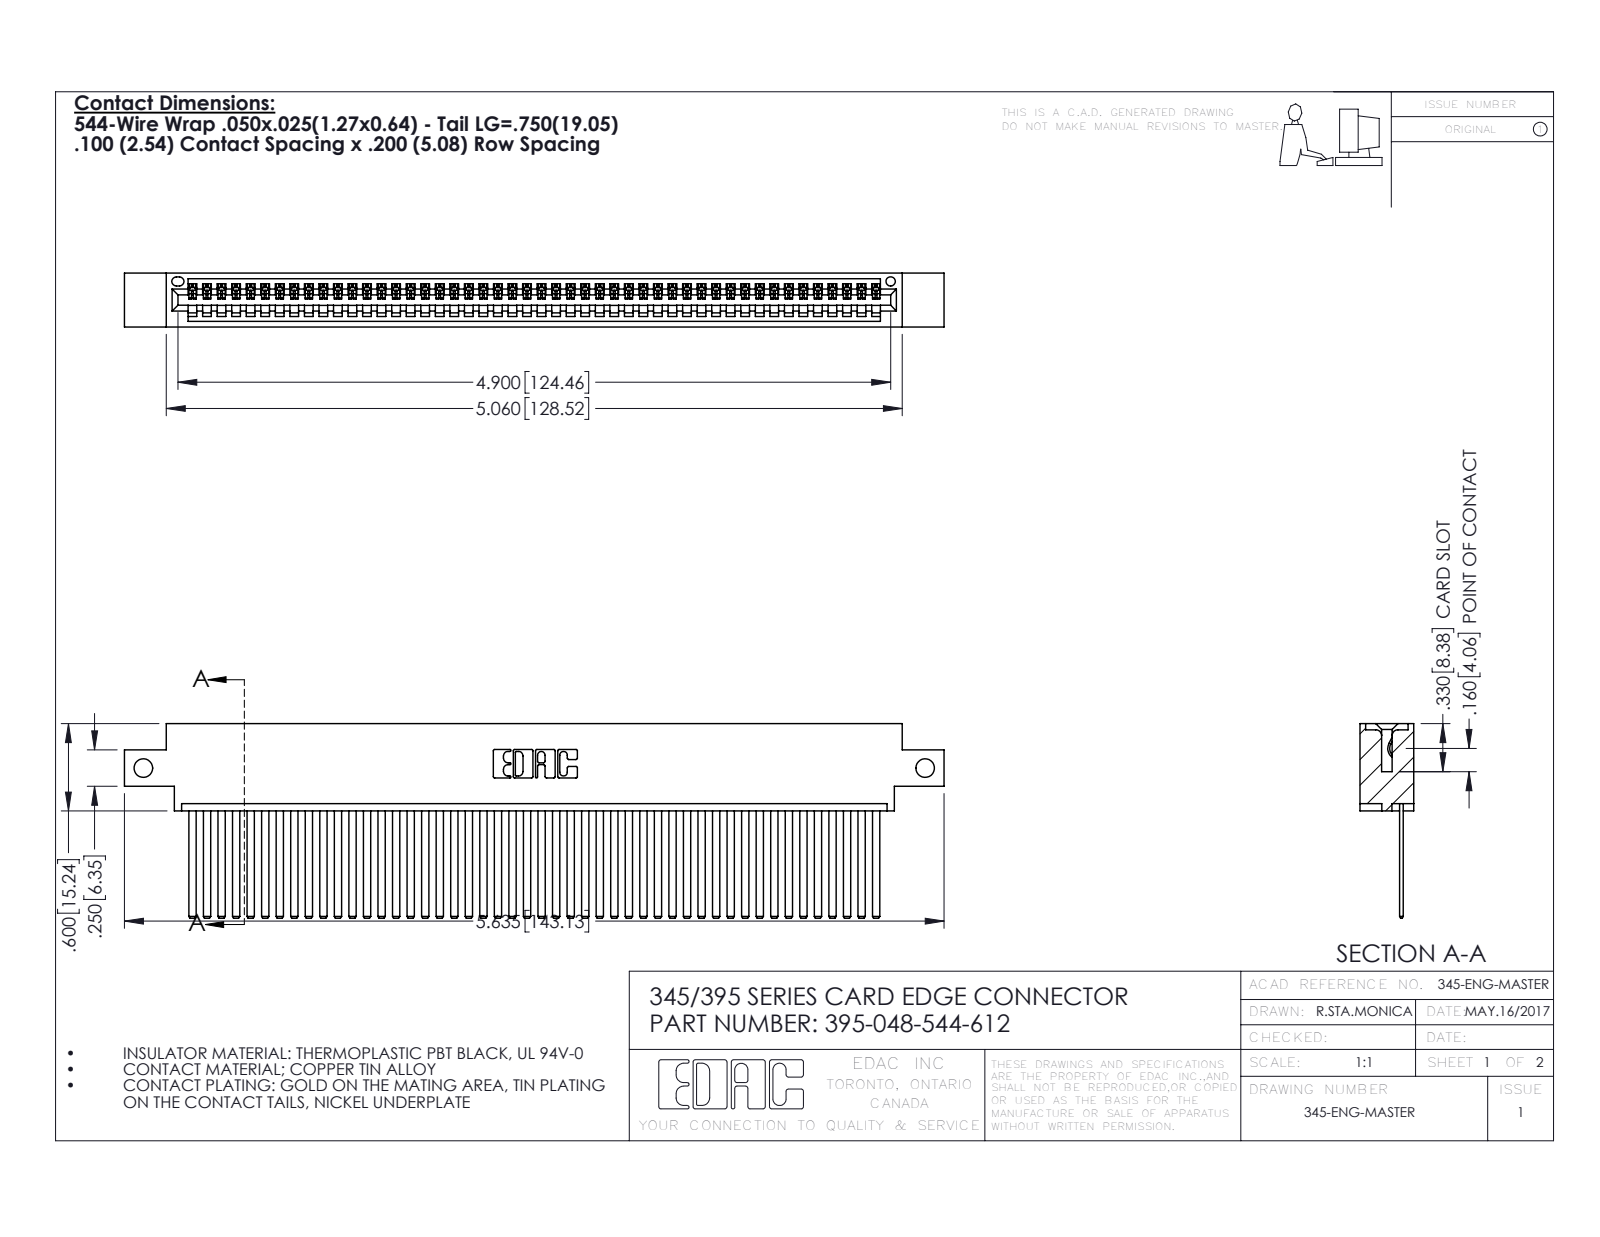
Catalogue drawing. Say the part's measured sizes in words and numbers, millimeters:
The part is named "345-292-001_345-293-144; 395-048-544-612; 345 Part_0.170 Offset - Side Mount". Its 3-D file was written by "SolidWorks 2016 (CONFIG_CONTROL_DESIGN)". It is 49 solids with 2626 faces: 1812 planar, 814 cylindrical and 0 other. Overall it measures 143.1 by 34 by 9.4 millimeters. Its volume is 14 000 cubic millimeters and its surface area 20 340 square millimeters. Round holes: 2 of diameter 3.3, 1 of diameter 1.6. Partial cylindrical surfaces (rounded edges, fillets, slot ends): 96 of radius 0.2, 22 of radius 0.3, 6 of radius 0.2, 6 of radius 0.8, 3 of radius 0.7, 2 of radius 0.8, 2 of radius 1, 1 of radius 0.4. The main face-to-face distances are 1.8, 7.6, 0.6, 2.5, 6.9, 9.4, 5.1, 5.7, 4.4, 3.8. The hole center spacings are 136.5.
